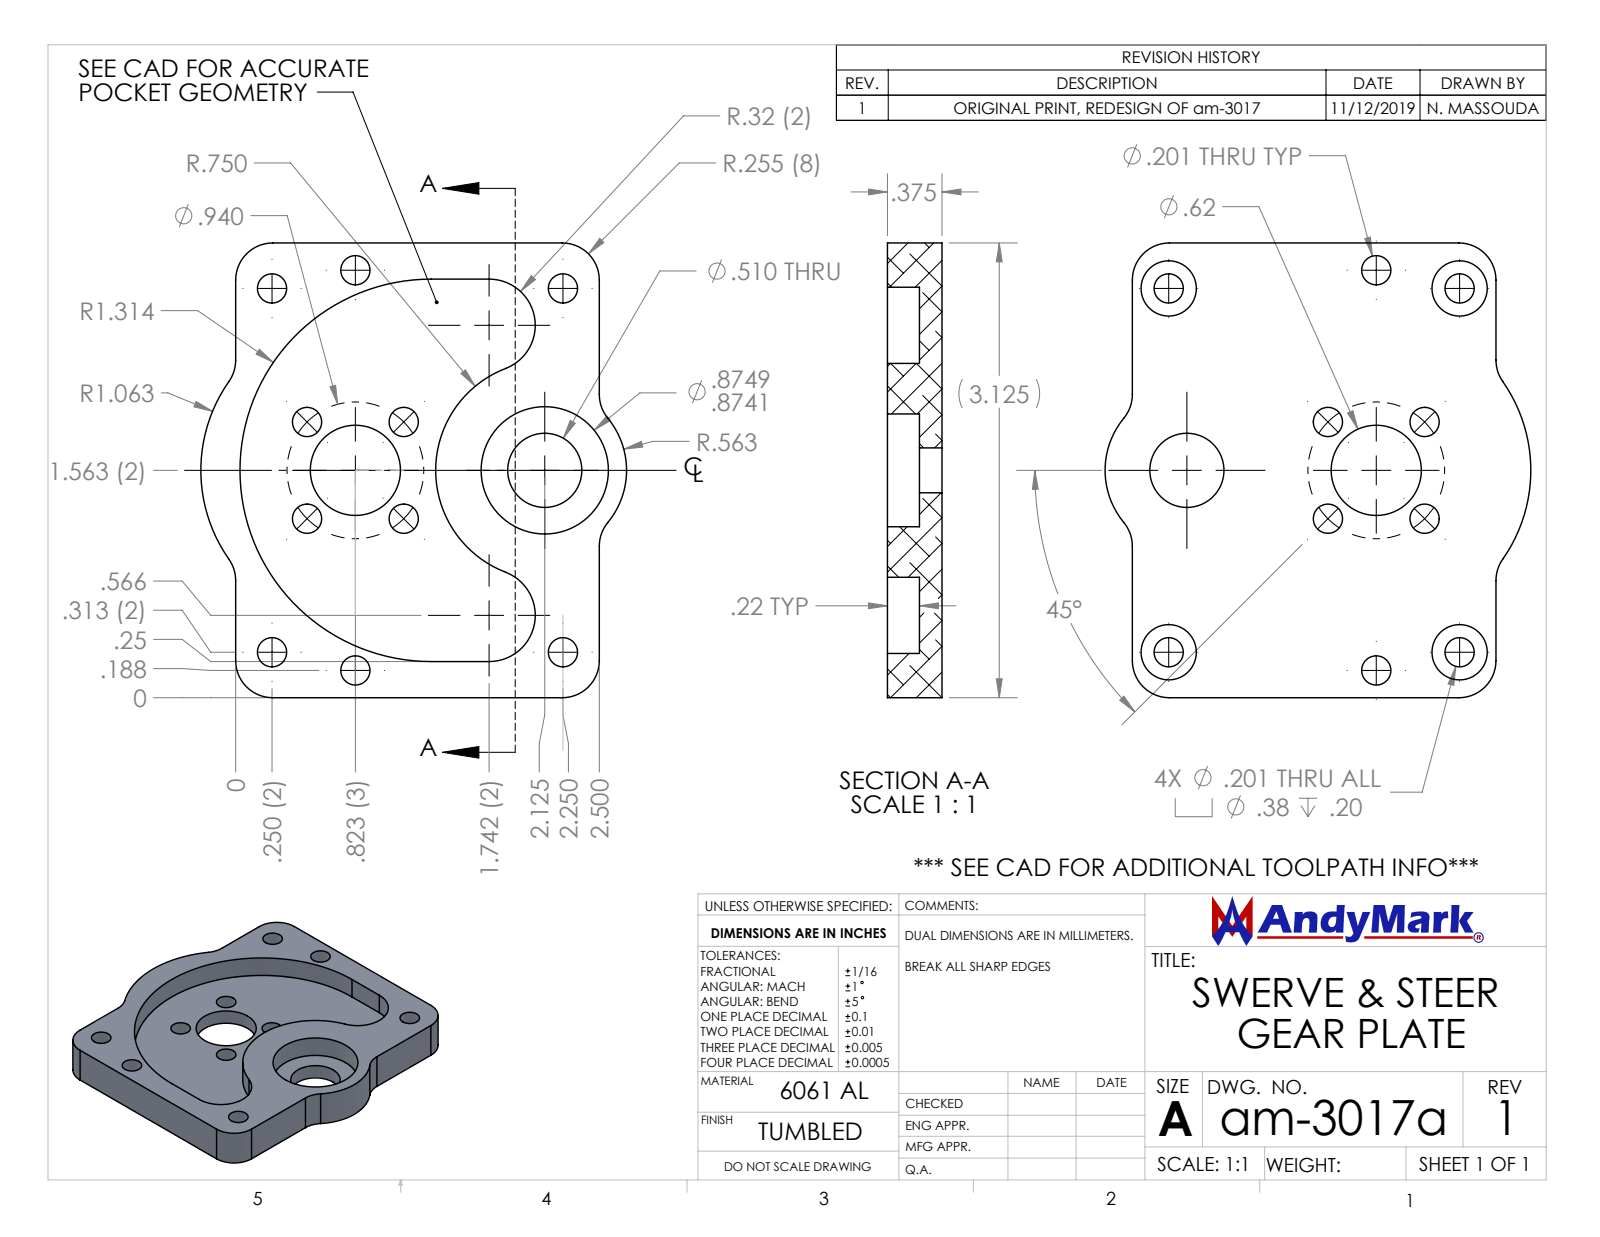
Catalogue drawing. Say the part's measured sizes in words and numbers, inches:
The part is named "am-3017a S&S Gear Plate". Its 3-D file was written by "SolidWorks 2019 (CONFIG_CONTROL_DESIGN)". It is 1 solid with 64 faces: 16 planar, 48 cylindrical and 0 other. Overall it measures 3.125 by 2.927 by 0.375 inches. Its volume is 1.843 cubic inches and its surface area 23.94 square inches. Round holes: 10 of diameter 0.201, 4 of diameter 0.38, 1 of diameter 0.51, 1 of diameter 0.62, 1 of diameter 0.875. Partial cylindrical surfaces (rounded edges, fillets, slot ends): 8 of radius 0.255, 2 of radius 0.318, 1 of radius 0.563, 1 of radius 0.75, 1 of radius 1.062, 1 of radius 1.314. The main face-to-face distances are 0.155, 0.375, 0.22, 3.125, 2.5, 0.2, 0.045, 0.175, 0.249, 2.877. The hole center spacings are 0.47, 1.375, 0.586, 0.665, 0.665, 0.94, 0.949, 1.025.
